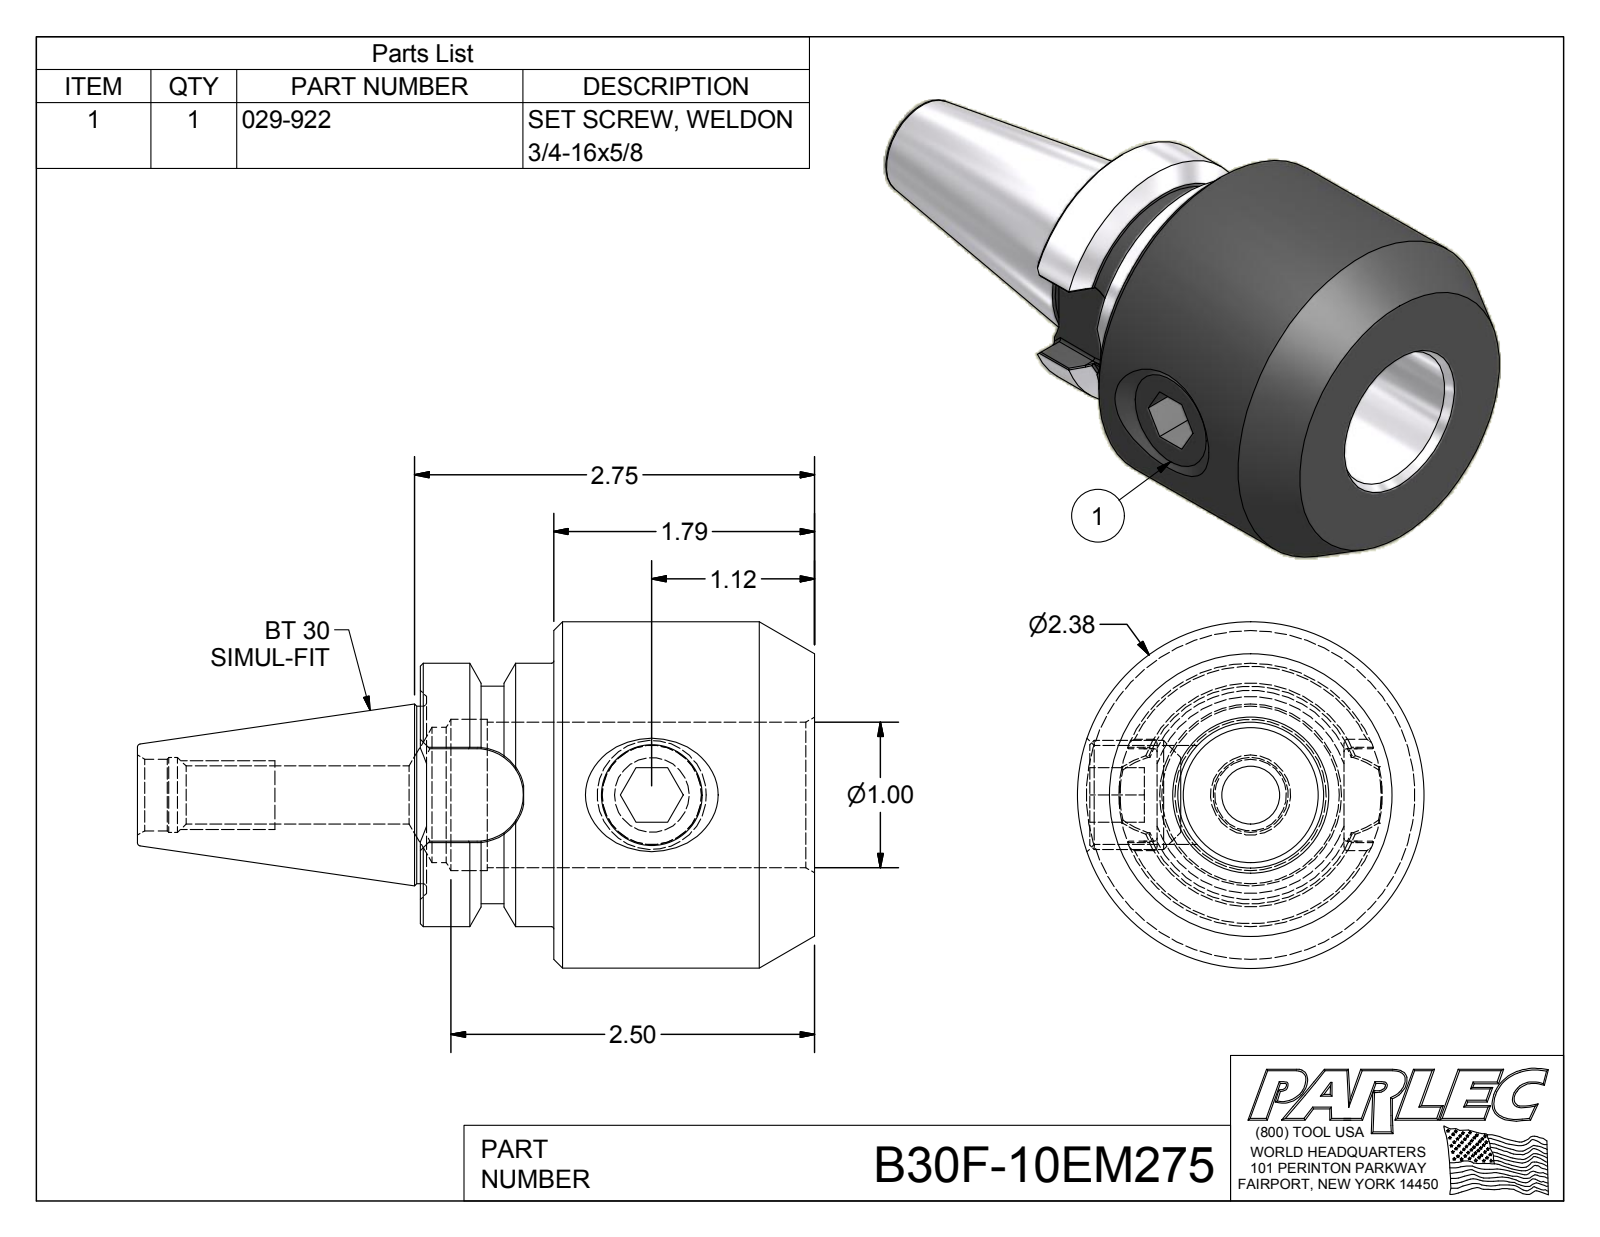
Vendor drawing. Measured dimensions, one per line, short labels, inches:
name: B30F-10EM275-1
written by: Autodesk Inventor 2018 (AUTOMOTIVE_DESIGN)
unit: in
bodies: 1 solid, 93 faces (27 planar, 24 cylindrical, 42 other)
size: 4.656 × 2.38 × 2.38
volume: 8.52 in³; area: 43.15 in²
holes: 1× ⌀0.398, 1× ⌀0.493, 1× ⌀0.517, 1× ⌀0.682, 1× ⌀0.93, 1× ⌀1, 1× ⌀1.04
bosses: 1× ⌀2.38, 1× ⌀1.811, 1× ⌀1.22
rounds: 8× R0.02, 1× R0.319, 1× R0.748
face distances: 1.794, 0.917, 2.711, 1.283, 0.042, 0.874, 2.669, 0.637, 1.945, 1.987
